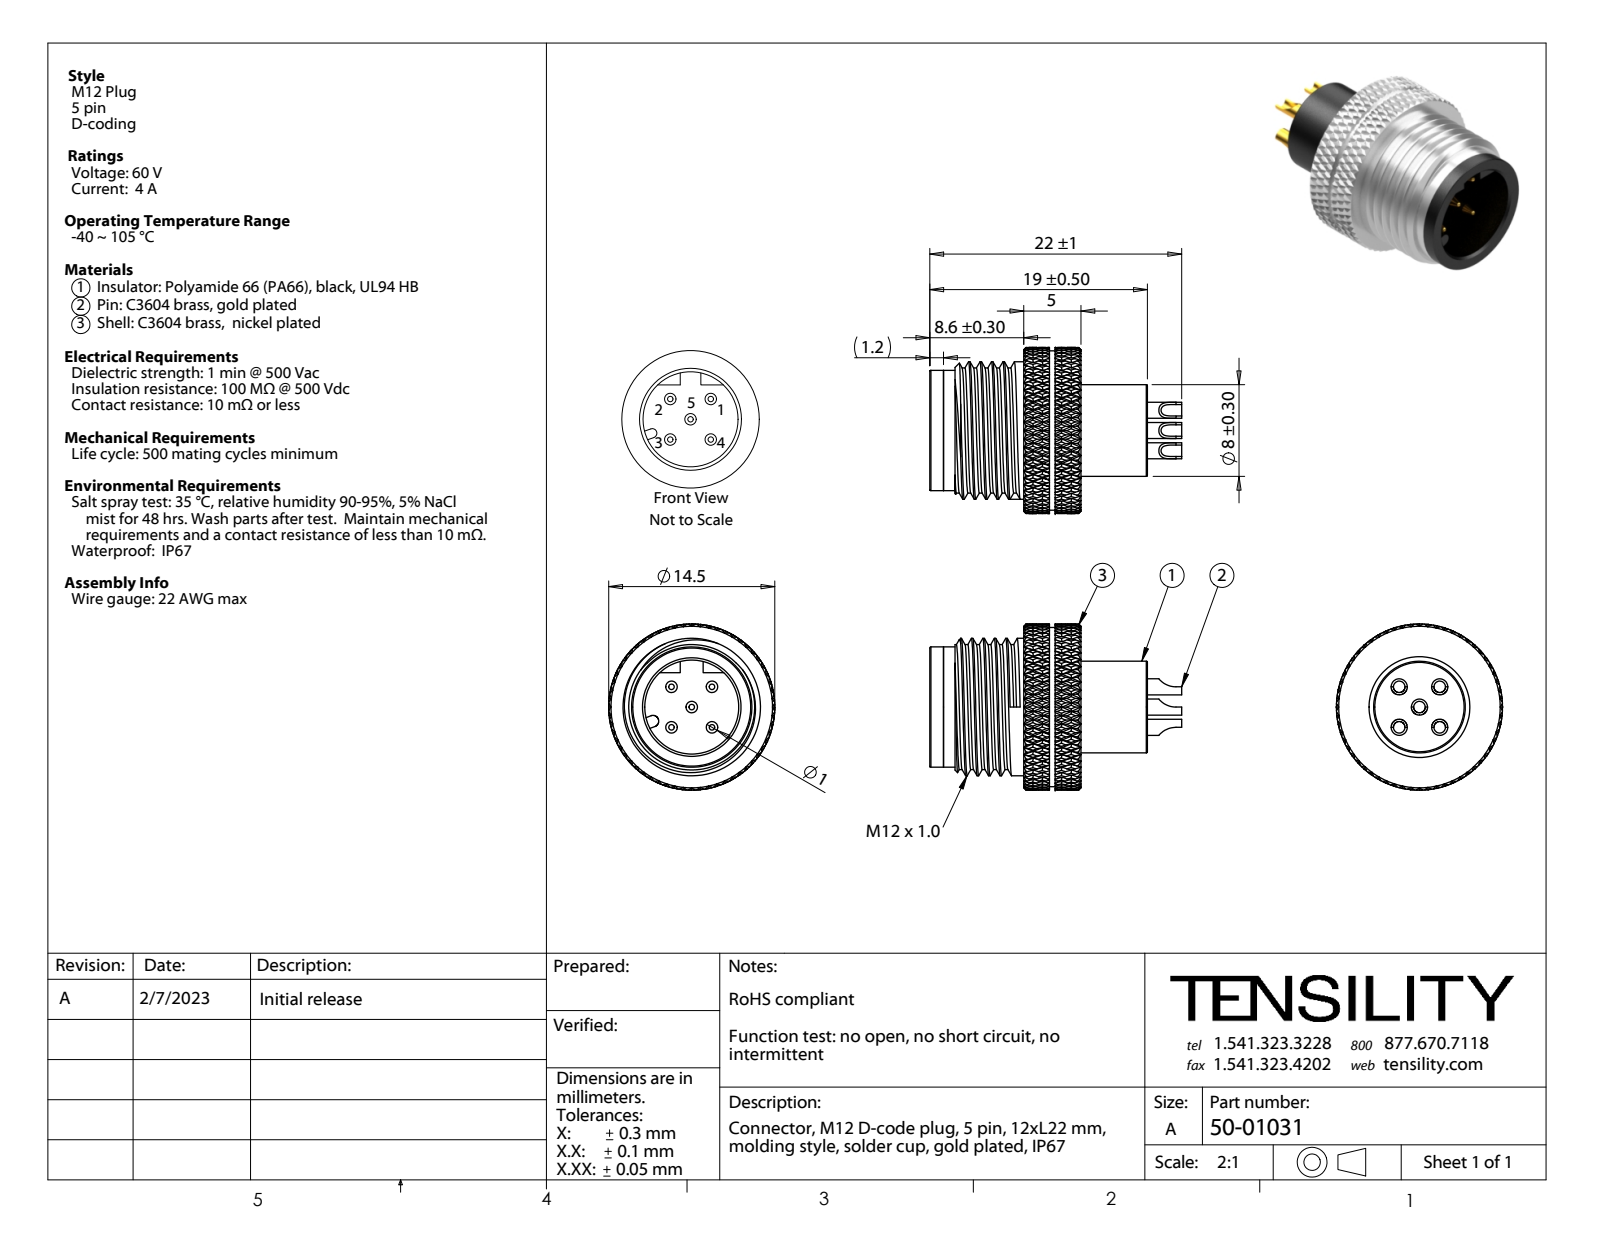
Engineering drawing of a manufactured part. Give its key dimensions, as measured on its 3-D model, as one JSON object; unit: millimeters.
{"part_name": "50-01031_revA; 50-01031-02; 50-01031-01; 50-01031-03", "step_written_by": "SolidWorks 2021 (CONFIG_CONTROL_DESIGN)", "units": "millimeters", "bodies": {"solids": 7, "faces": 2301, "planar": 62, "cylindrical": 597, "other": 1642}, "overall_size": [22, 14.5, 14.5], "volume_mm3": 1385, "surface_area_mm2": 2806, "round_holes": [[1, 5], [8.2, 1], [8.8, 1], [9.5, 1]], "round_bosses_or_shafts": [[1.4, 5], [14.5, 1], [13.9, 1], [12, 1], [10.5, 1], [9, 1], [8, 1]], "partial_cylinders_radius": [[1.96, 3], [0.5, 1]], "face_to_face_distances": [12, 10, 10.8, 7, 5, 0.8, 4.2, 7.8, 5.8, 17.8], "hole_center_spacings": [2.5, 3.54, 5.01]}
